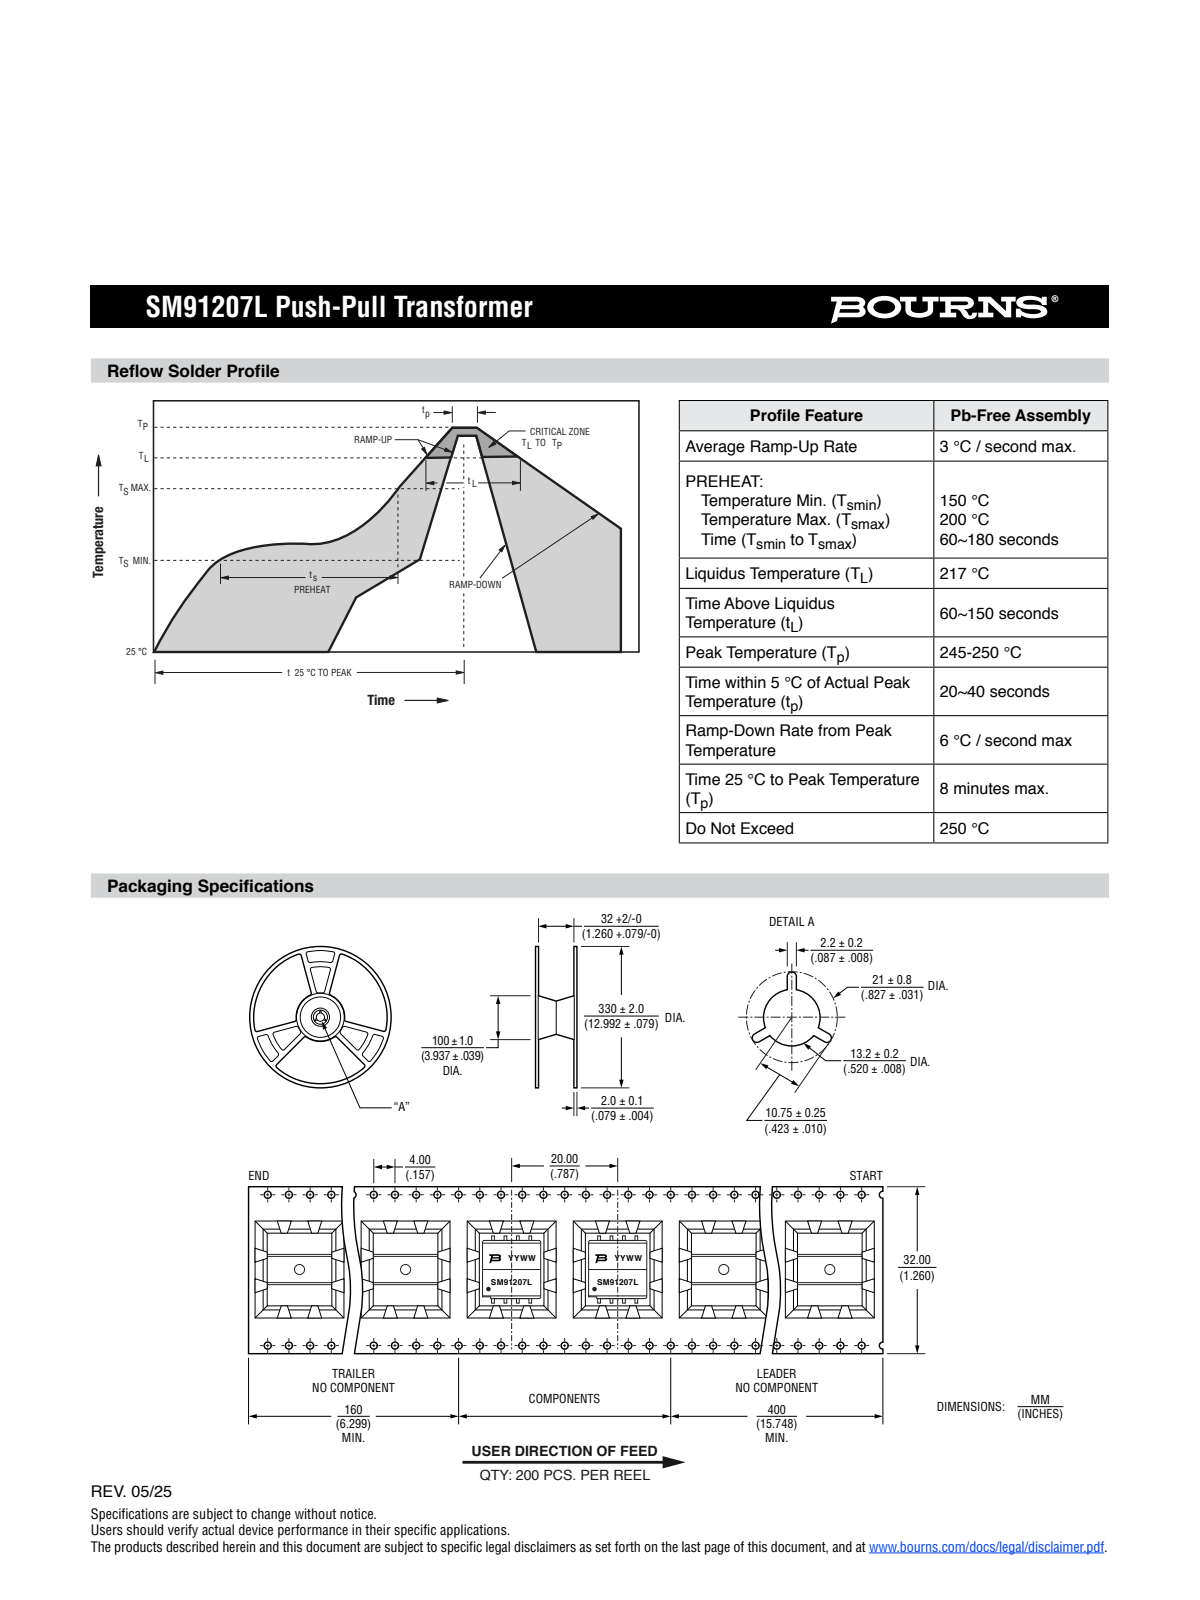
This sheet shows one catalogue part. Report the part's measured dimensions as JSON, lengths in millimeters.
{"part_name": "SM91207L", "step_written_by": "Autodesk Inventor 2023 (AUTOMOTIVE_DESIGN)", "units": "millimeters", "bodies": {"solids": 1, "faces": 411, "planar": 235, "cylindrical": 85, "other": 91}, "overall_size": [13.2, 11.8, 11.62], "volume_mm3": 1083, "surface_area_mm2": 892, "round_bosses_or_shafts": [[1, 1]], "partial_cylinders_radius": [[0.3, 25], [0.2, 22], [0.15, 2], [0.65, 2], [0.12, 1], [0.13, 1], [0.42, 1], [0.46, 1]], "face_to_face_distances": [7.65, 10.4, 11.8, 0.5, 10, 2.1, 2.35, 7.9, 10.9, 2.3]}
